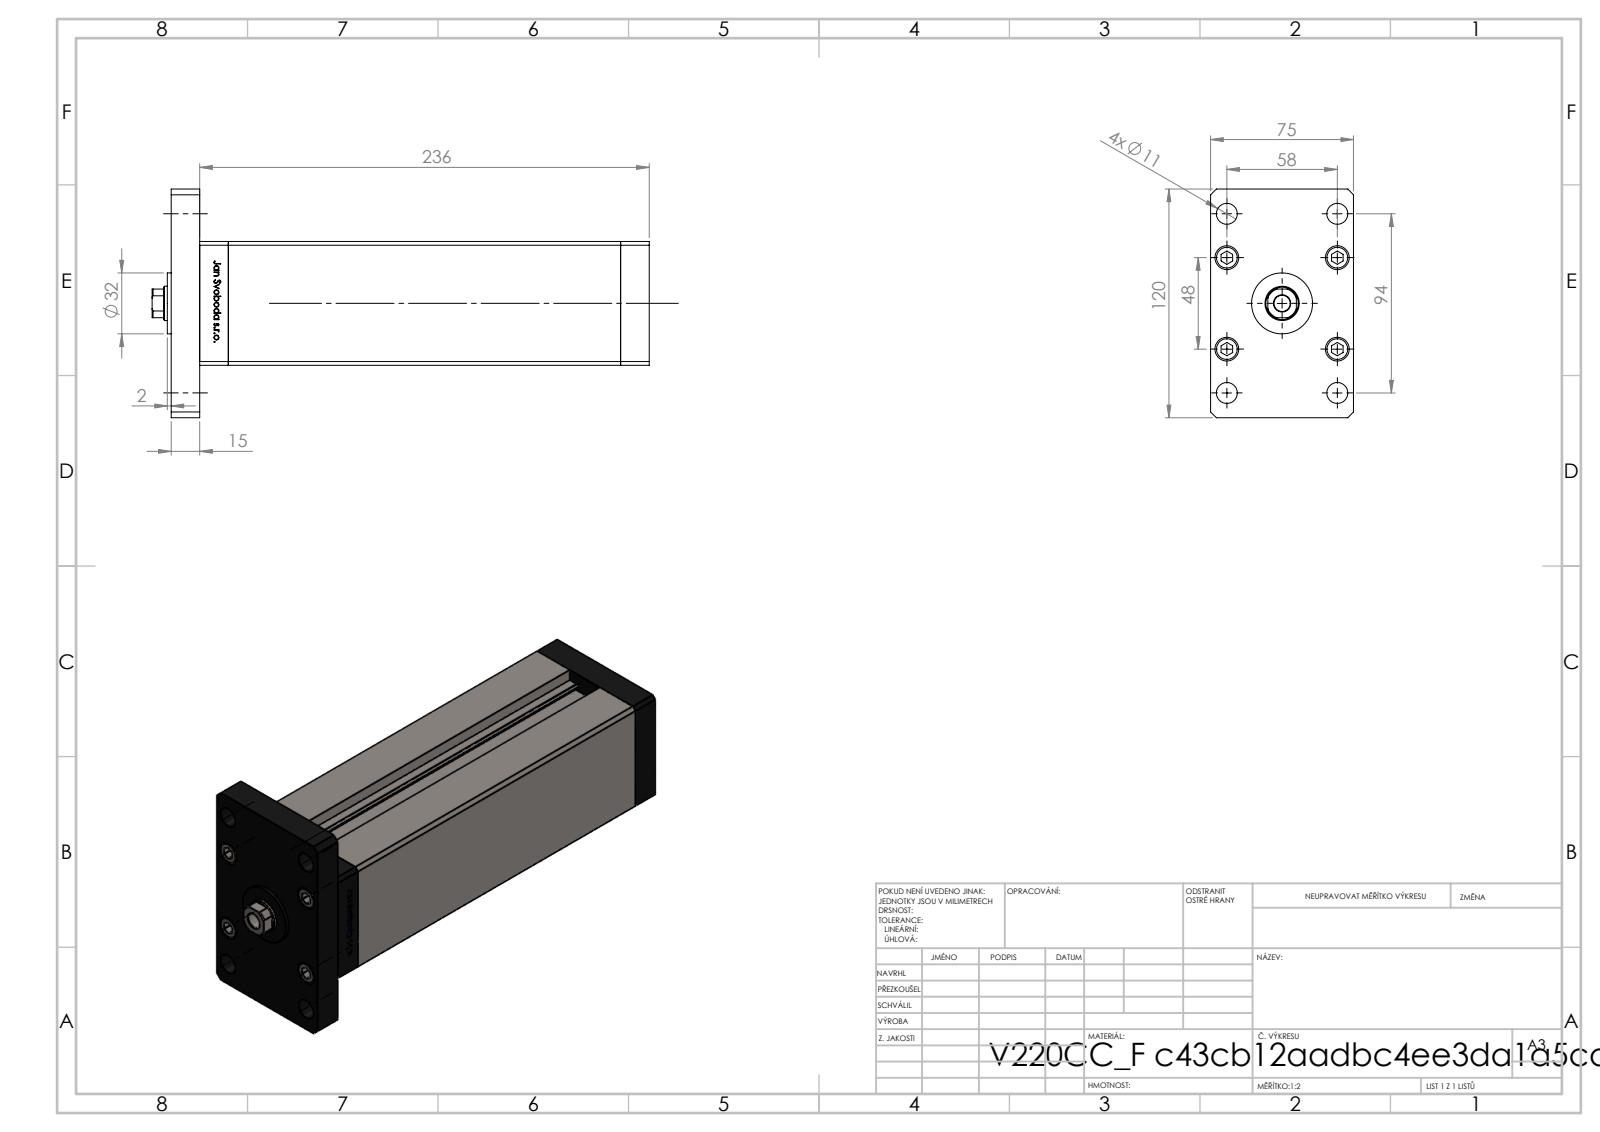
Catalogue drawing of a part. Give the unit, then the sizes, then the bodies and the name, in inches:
Units: inches
Overall size (bounding box): 10.276 × 4.724 × 2.953
Round holes (diameter × count): ⌀0.354 ×5, ⌀0.531 ×5, ⌀0.315 ×4, ⌀0.433 ×4, ⌀0.492 ×4, ⌀0.079 ×2, ⌀0.518 ×2, ⌀0.335 ×1, ⌀0.709 ×1, ⌀0.768 ×1
Round bosses / shafts (diameter × count): ⌀0.492 ×5, ⌀0.315 ×5, ⌀1.26 ×1
Partial cylindrical surfaces — rounded edges, fillets, slot ends (radius × count): R0.037 ×2, R0.335 ×1
Main face-to-face distances: 0.591, 2.953, 2.559, 8.701, 9.291, 1.181, 8.11, 9.882, 0.512, 2.146
Hole centre spacings: 0.945, 0.906, 1.482, 2.174, 2.283, 2.456, 2.795, 3.609
Volume: 69.38 in³ · Surface area: 297.5 in²
Bodies: 19 solids, 1308 faces (515 planar, 187 cylindrical, 606 other)
Part name (STEP PRODUCT): V220C_F; V220C BACK_F; V220C_VC_F; V220C_F_MIDDLE (+2 more)
STEP written by: SolidWorks 2019 (CONFIG_CONTROL_DESIGN)
